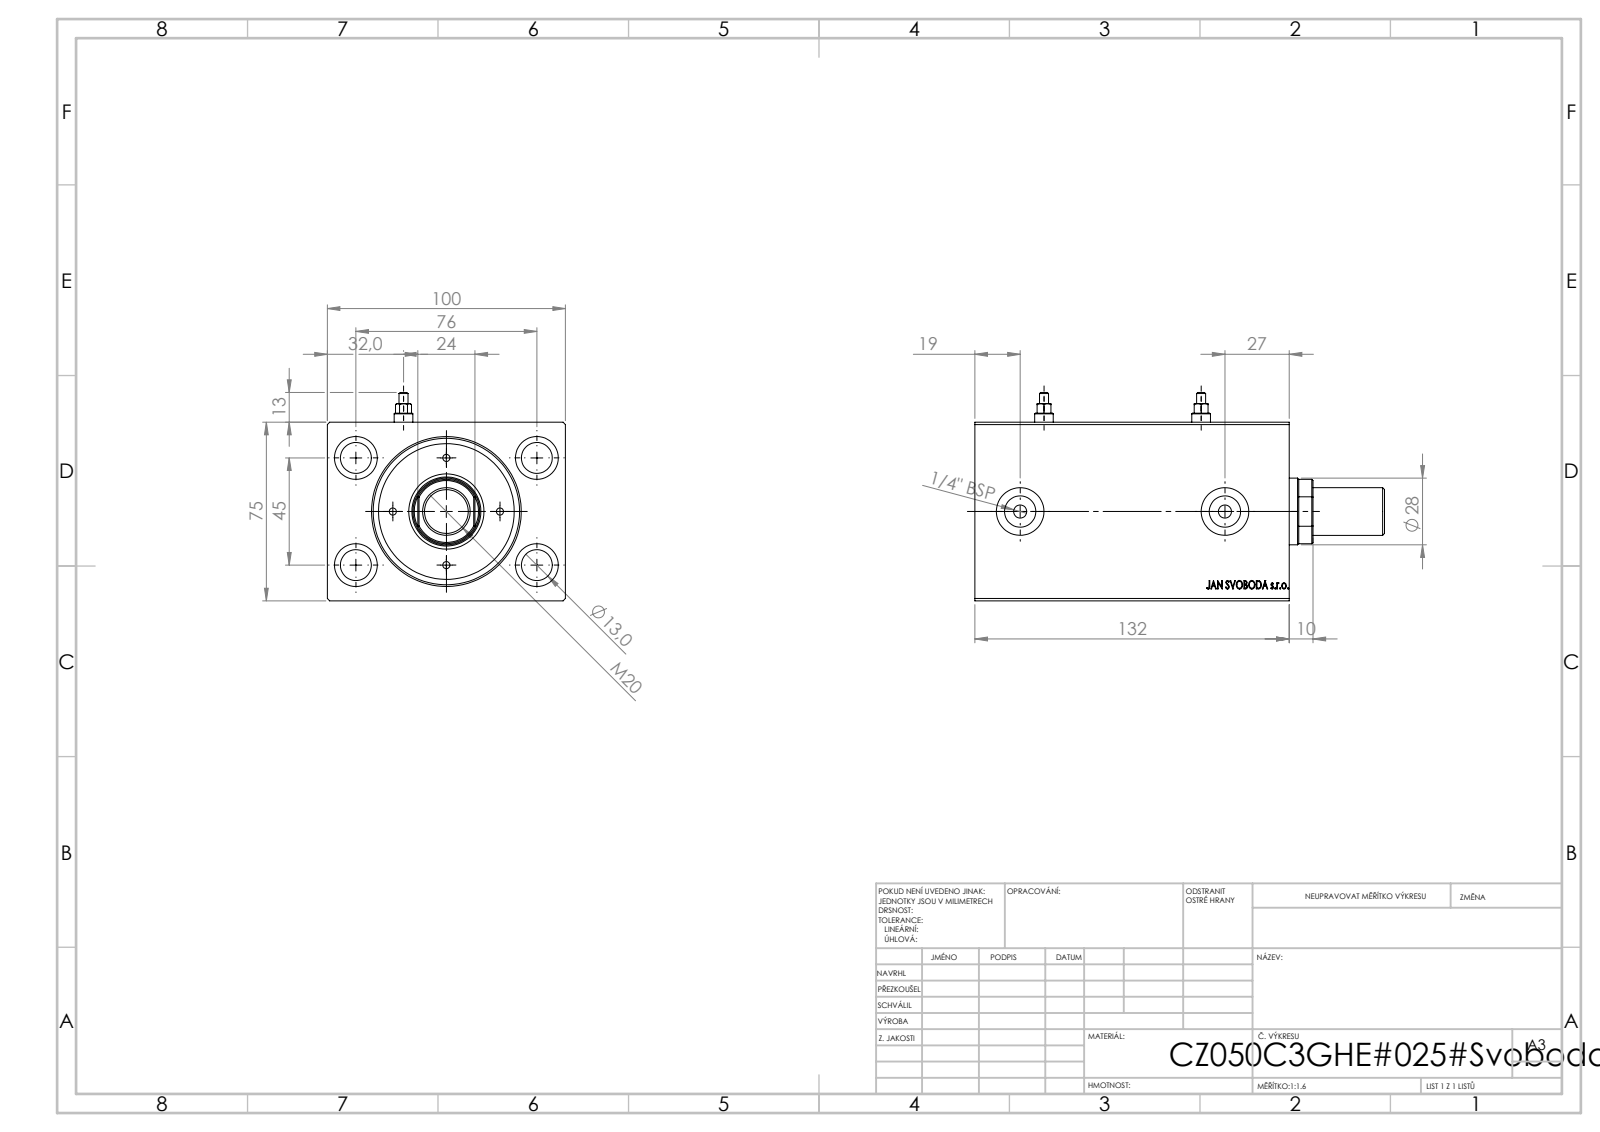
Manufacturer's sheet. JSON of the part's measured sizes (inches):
{"step_written_by": "SolidWorks 2019 (CONFIG_CONTROL_DESIGN)", "units": "inches", "bodies": {"solids": 1, "faces": 825, "planar": 397, "cylindrical": 46, "other": 382}, "overall_size": [5.197, 3.937, 2.953], "volume_in3": 40.94, "surface_area_in2": 158.9, "round_holes": [[0.512, 4], [0.709, 4], [0.217, 2], [0.315, 2], [0.518, 2], [0.787, 2], [1.417, 1], [1.969, 1], [2.421, 1]], "face_to_face_distances": [2.953, 3.937, 5.197, 4.496, 0.701, 5.189, 0.693, 0.394, 4.102, 4.795], "hole_center_spacings": [1.739, 1.772, 2.992, 3.477, 2.598, 3.386]}
